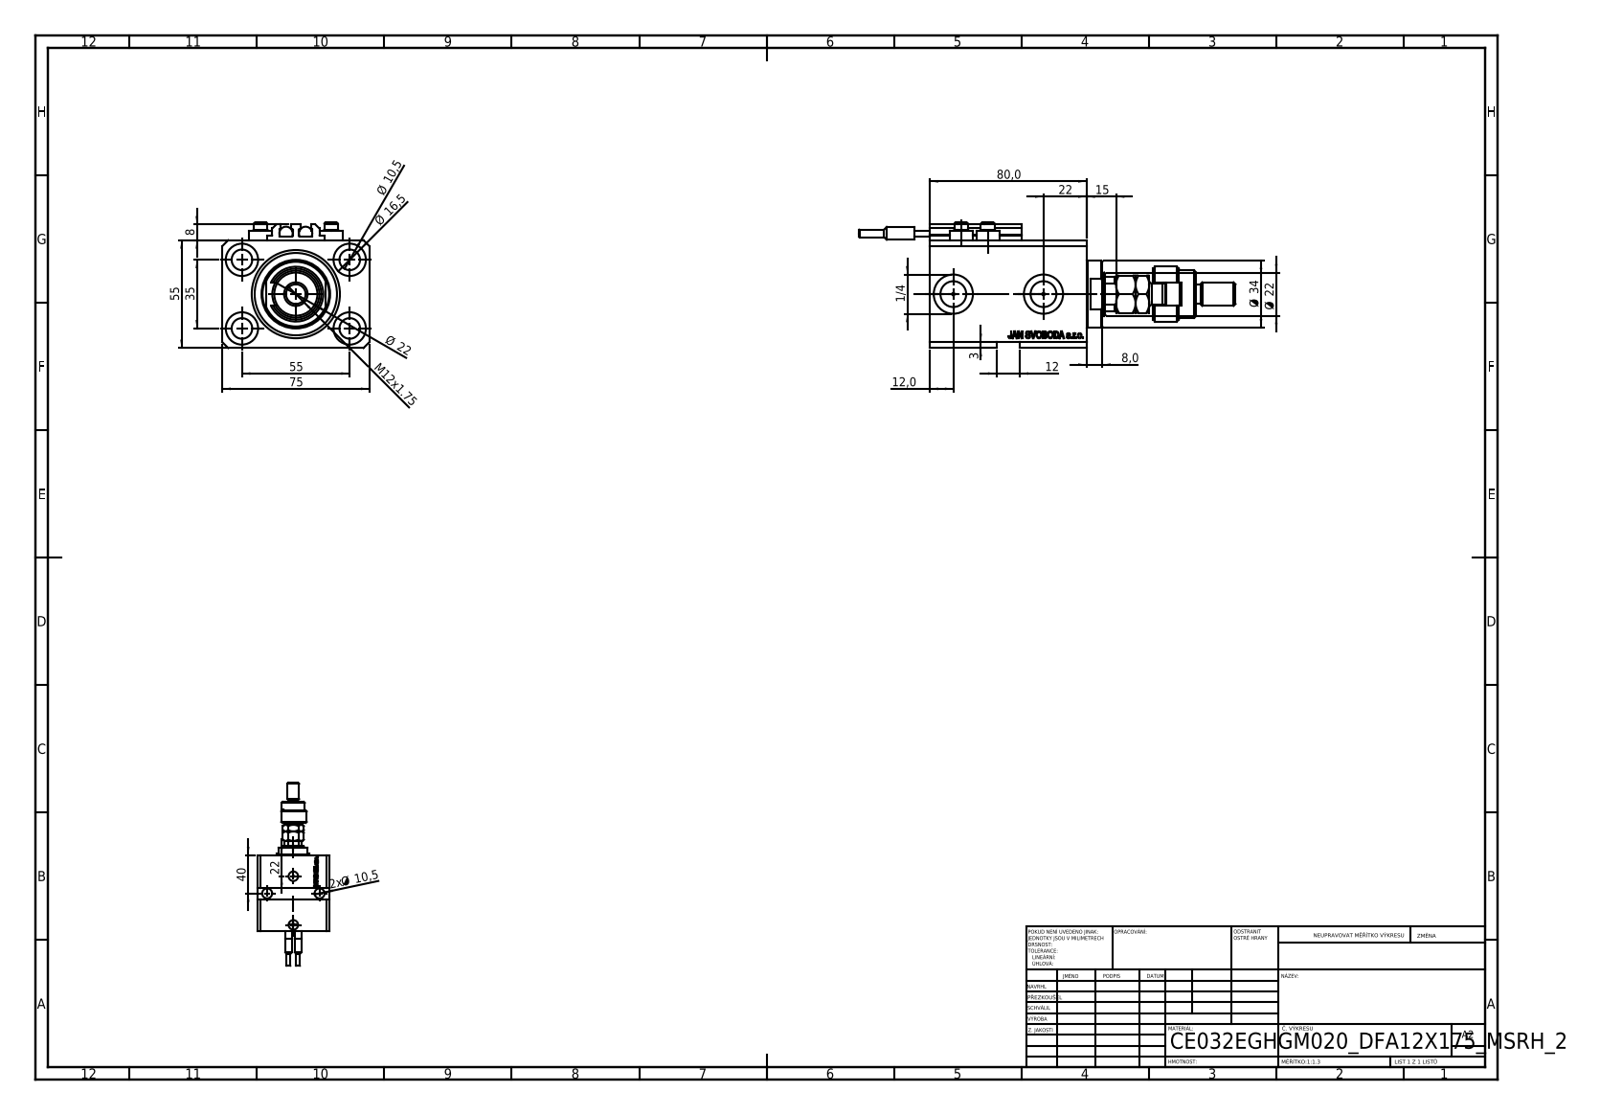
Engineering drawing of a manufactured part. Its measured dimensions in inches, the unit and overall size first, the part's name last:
Units: inches
Overall size (bounding box): 7.559 × 2.953 × 2.52
Round holes (diameter × count): ⌀0.413 ×7, ⌀0.049 ×4, ⌀0.157 ×4, ⌀0.65 ×4, ⌀0.394 ×2, ⌀0.518 ×2, ⌀0.787 ×2, ⌀0.866 ×1, ⌀1.26 ×1, ⌀1.772 ×1
Round bosses / shafts (diameter × count): ⌀0.457 ×4, ⌀0.276 ×4, ⌀0.268 ×2, ⌀0.256 ×2, ⌀0.157 ×2, ⌀1.339 ×1, ⌀1.102 ×1, ⌀0.945 ×1
Partial cylindrical surfaces — rounded edges, fillets, slot ends (radius × count): R0.008 ×10, R0.384 ×1, R0.413 ×1
Main face-to-face distances: 2.165, 2.953, 0.591, 3.15, 0.118, 2.559, 2.169, 0.39, 2.244, 2.76
Hole centre spacings: 1.283, 2.165, 0.535, 0.555, 0.783, 0.792, 1.016, 1.121
Volume: 18.63 in³ · Surface area: 130.7 in²
Bodies: 12 solids, 1201 faces (574 planar, 151 cylindrical, 476 other)
Part name (STEP PRODUCT): MFA; SWITCH_V250CE; V250CE_C_VCP; V250CE_VC_E (+3 more)
STEP written by: SolidWorks 2019 (CONFIG_CONTROL_DESIGN)
